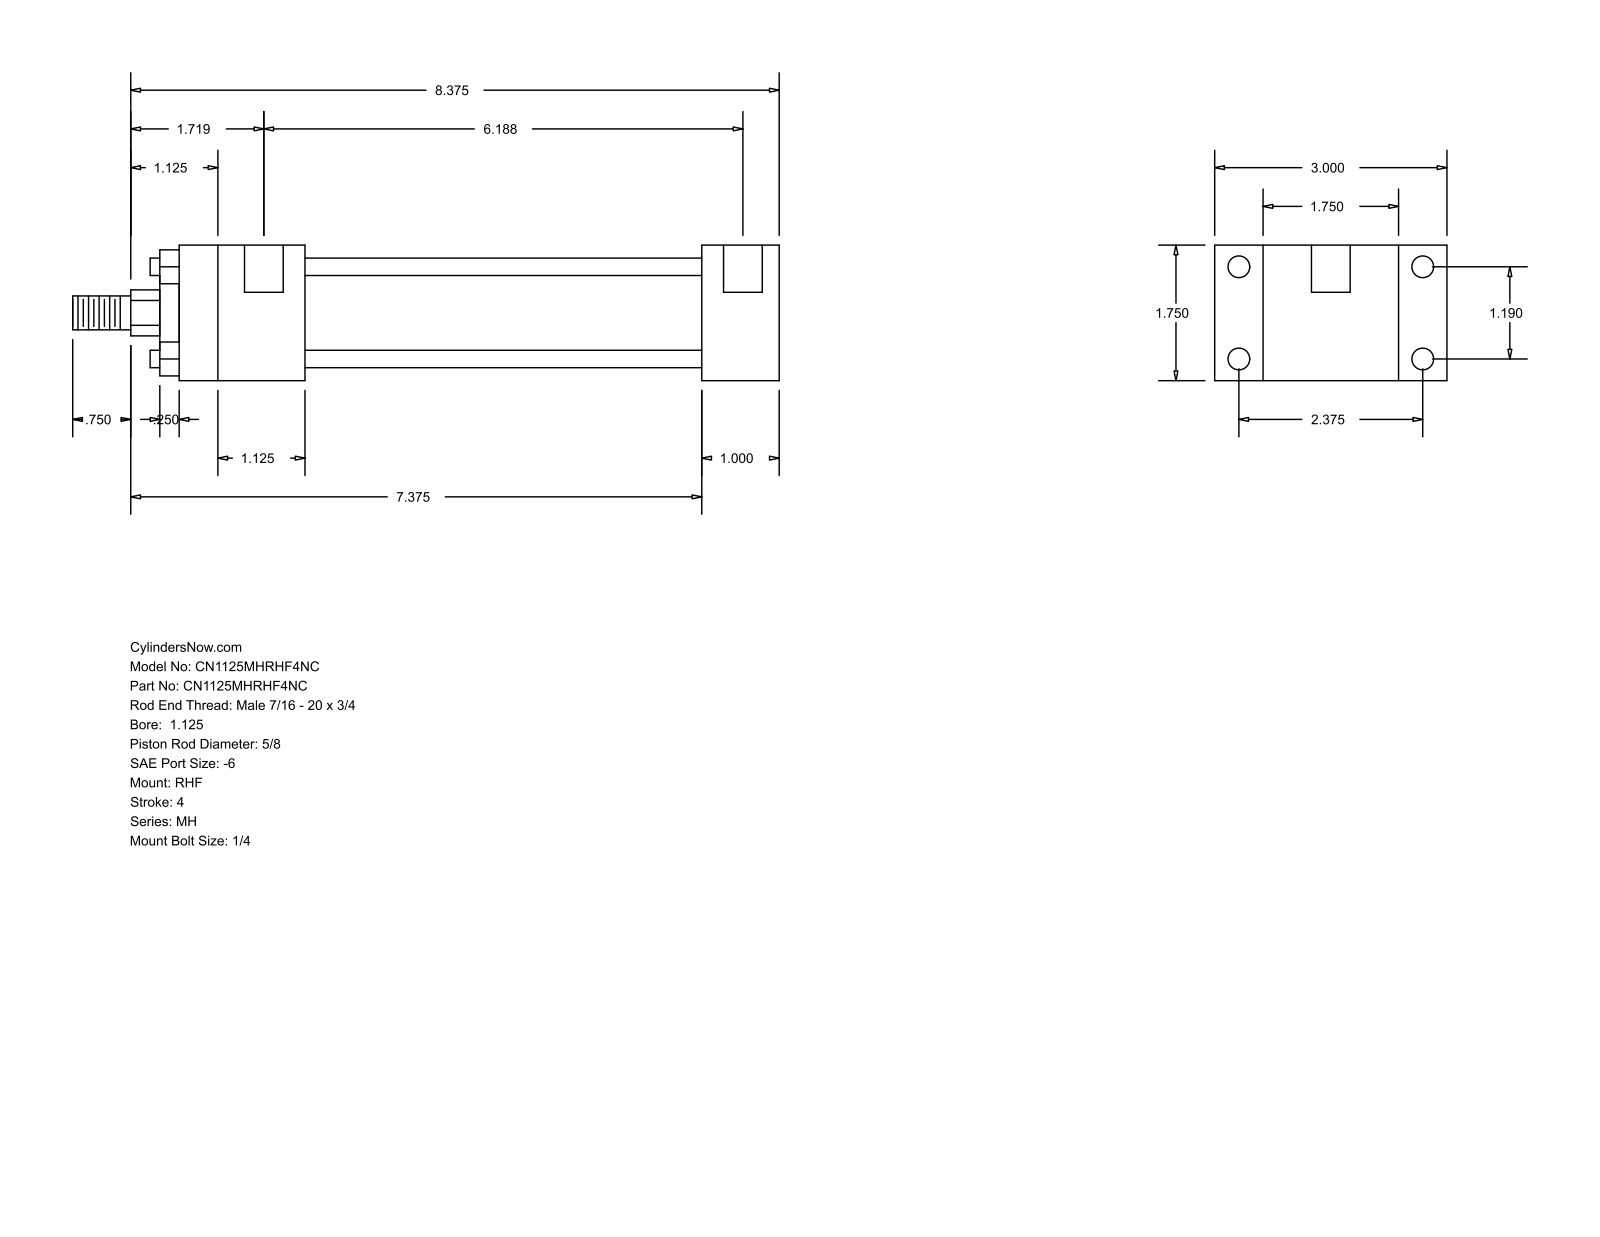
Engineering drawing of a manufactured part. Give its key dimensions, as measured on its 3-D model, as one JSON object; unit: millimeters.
{"part_name": "MH_RHF__0112_0.625", "step_written_by": "GSSL Pune (CONFIG_CONTROL_DESIGN)", "units": "millimeters", "bodies": {"solids": 0, "faces": 88, "planar": 60, "cylindrical": 28, "other": 0}, "overall_size": [231.78, 76.2, 44.45], "round_holes": [[5.56, 4], [7.14, 4], [12.7, 2]], "round_bosses_or_shafts": [[5.71, 4], [34.92, 1], [28.57, 1], [15.88, 1], [11.11, 1]], "partial_cylinders_radius": [[7.54, 1]], "face_to_face_distances": [44.46, 15.87, 25.4, 60.33, 76.2, 130.17, 155.57, 41.27, 171.44, 196.84], "hole_center_spacings": [30.22, 60.32, 67.47, 153.99, 3.17, 157.16]}
